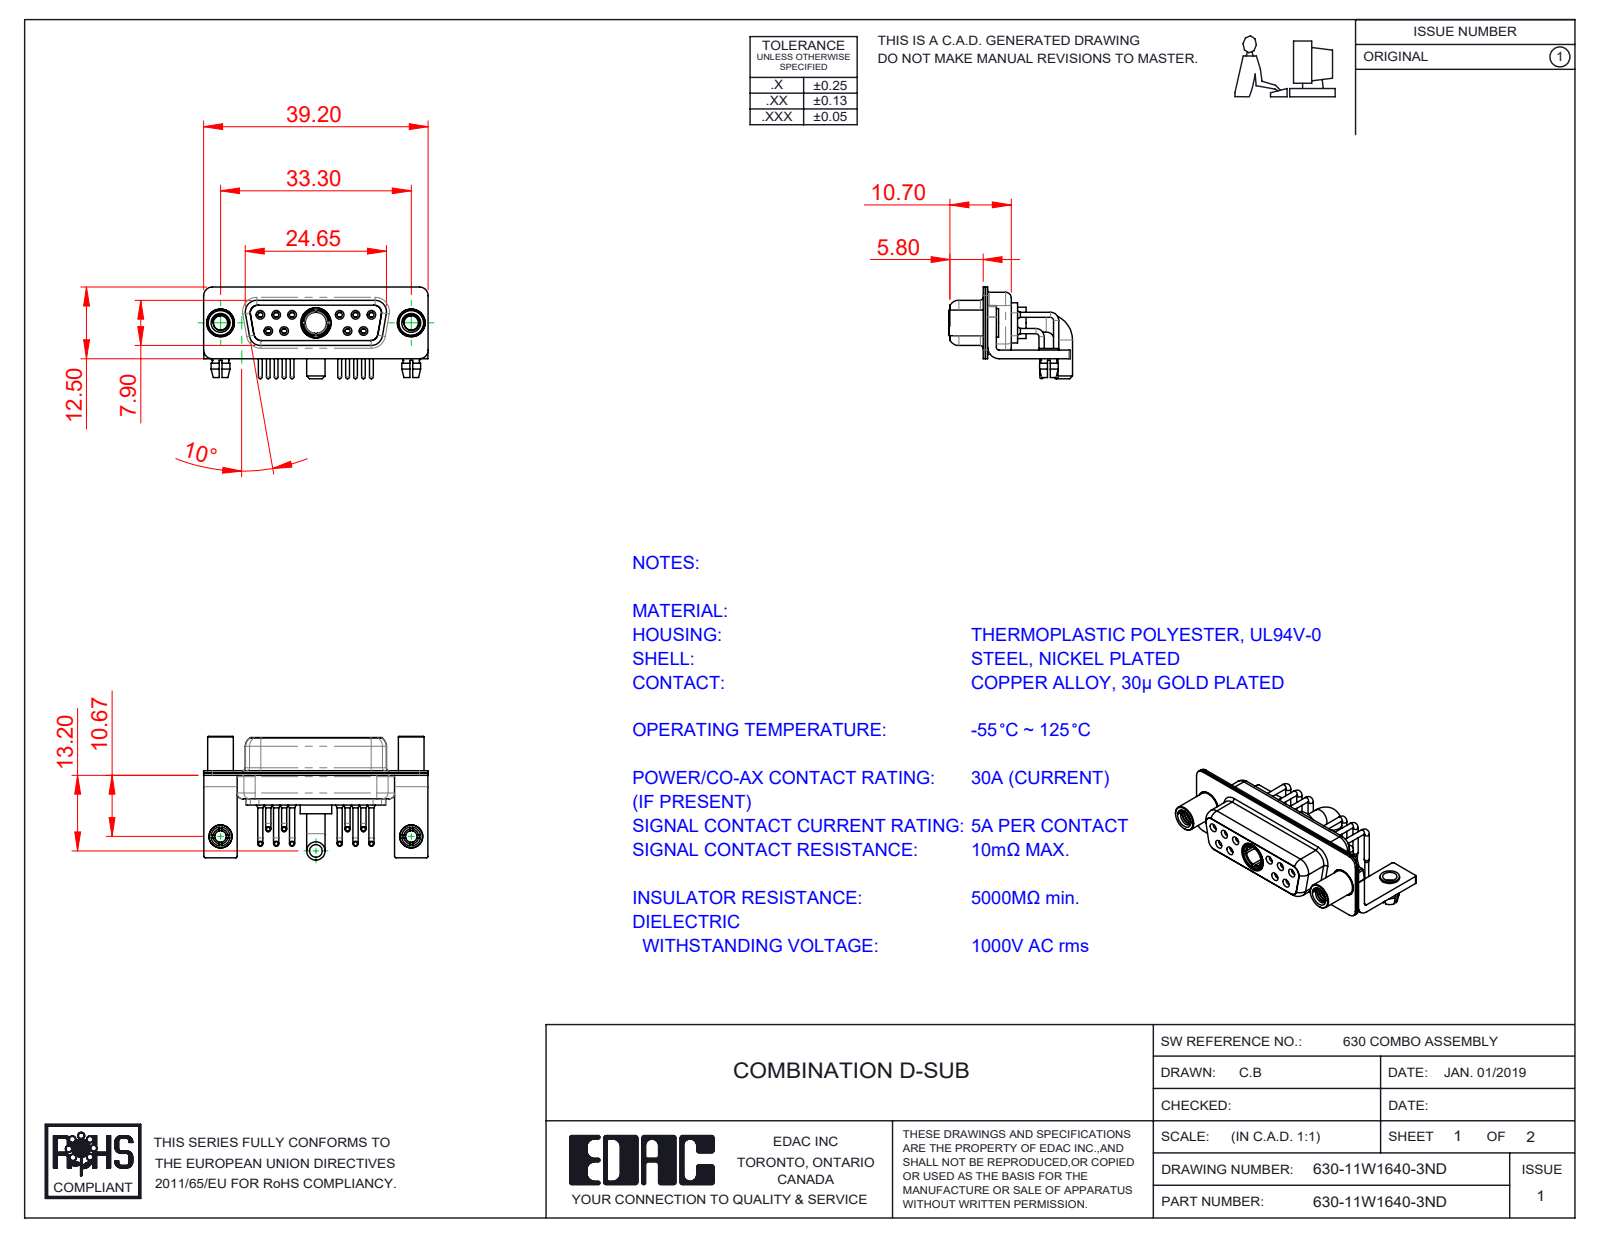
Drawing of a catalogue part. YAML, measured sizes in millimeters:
part_name: "630Combo Housing_11W1; 630Combo Shell Front_15 Contacts; 630Combo Shell Rear_15 Contacts; 630Combo Threaded Standoff_D (+6 more)"
step_written_by: "SolidWorks 2020 (CONFIG_CONTROL_DESIGN)"
units: millimeters
bodies: {solids: 21, faces: 1077, planar: 316, cylindrical: 496, other: 265}
overall_size: [39.2, 21.6, 16]
volume: 3094
surface_area: 7425
round_holes:
  - {diameter: 2, count: 12}
  - {diameter: 0.9, count: 10}
  - {diameter: 1.1, count: 10}
  - {diameter: 1.5, count: 10}
  - {diameter: 1.7, count: 6}
  - {diameter: 1.6, count: 4}
  - {diameter: 2.5, count: 4}
  - {diameter: 4.85, count: 3}
  - {diameter: 3.2, count: 2}
  - {diameter: 4, count: 2}
  - {diameter: 4.05, count: 2}
  - {diameter: 3.7, count: 1}
round_bosses_or_shafts:
  - {diameter: 0.9, count: 10}
  - {diameter: 0.65, count: 10}
  - {diameter: 1.6, count: 6}
  - {diameter: 5, count: 2}
  - {diameter: 4.95, count: 2}
  - {diameter: 4.8, count: 2}
  - {diameter: 4.5, count: 2}
  - {diameter: 4, count: 2}
partial_cylinders:
  - {radius: 0.25, count: 16}
  - {radius: 1.5, count: 16}
  - {radius: 2, count: 13}
  - {radius: 1.35, count: 12}
  - {radius: 1.6, count: 8}
  - {radius: 0.5, count: 5}
  - {radius: 0.6, count: 4}
  - {radius: 0.65, count: 4}
face_to_face_distances: [0.4, 0.8, 0.45, 1.4, 8.45, 1.5, 1.8, 8.9, 6.2, 2.3]
hole_center_spacings: [3.16, 2.77, 13.85, 11.08, 16.62, 5.03, 5.04, 5.54]
